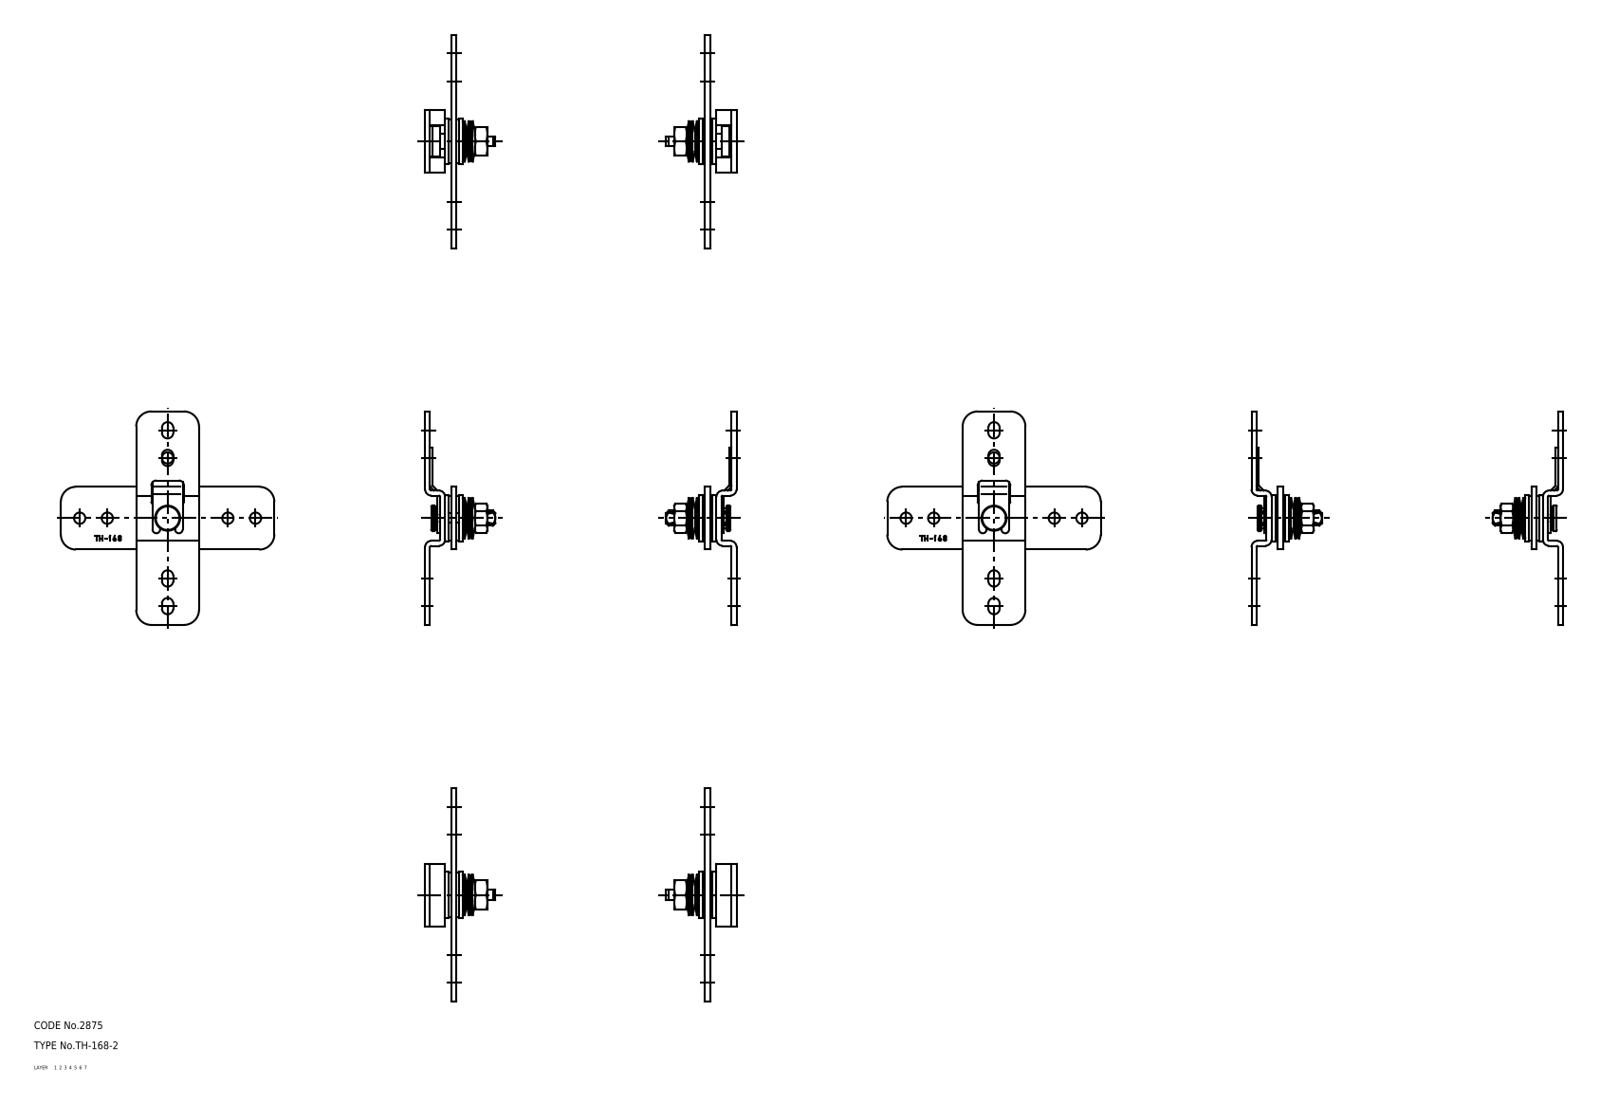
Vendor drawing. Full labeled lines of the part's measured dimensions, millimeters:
Part name (STEP PRODUCT): 67125405; 67125418; 67125431; 67125444 (+2 more)
STEP written by: CADfix (AUTOMOTIVE_DESIGN)
Units: millimetres
Bodies: 6 solids, 326 faces (0 planar, 0 cylindrical, 326 other)
Overall size (bounding box): 124 × 85 × 85
Volume: 22 299 mm³ · Surface area: 22 965 mm²
